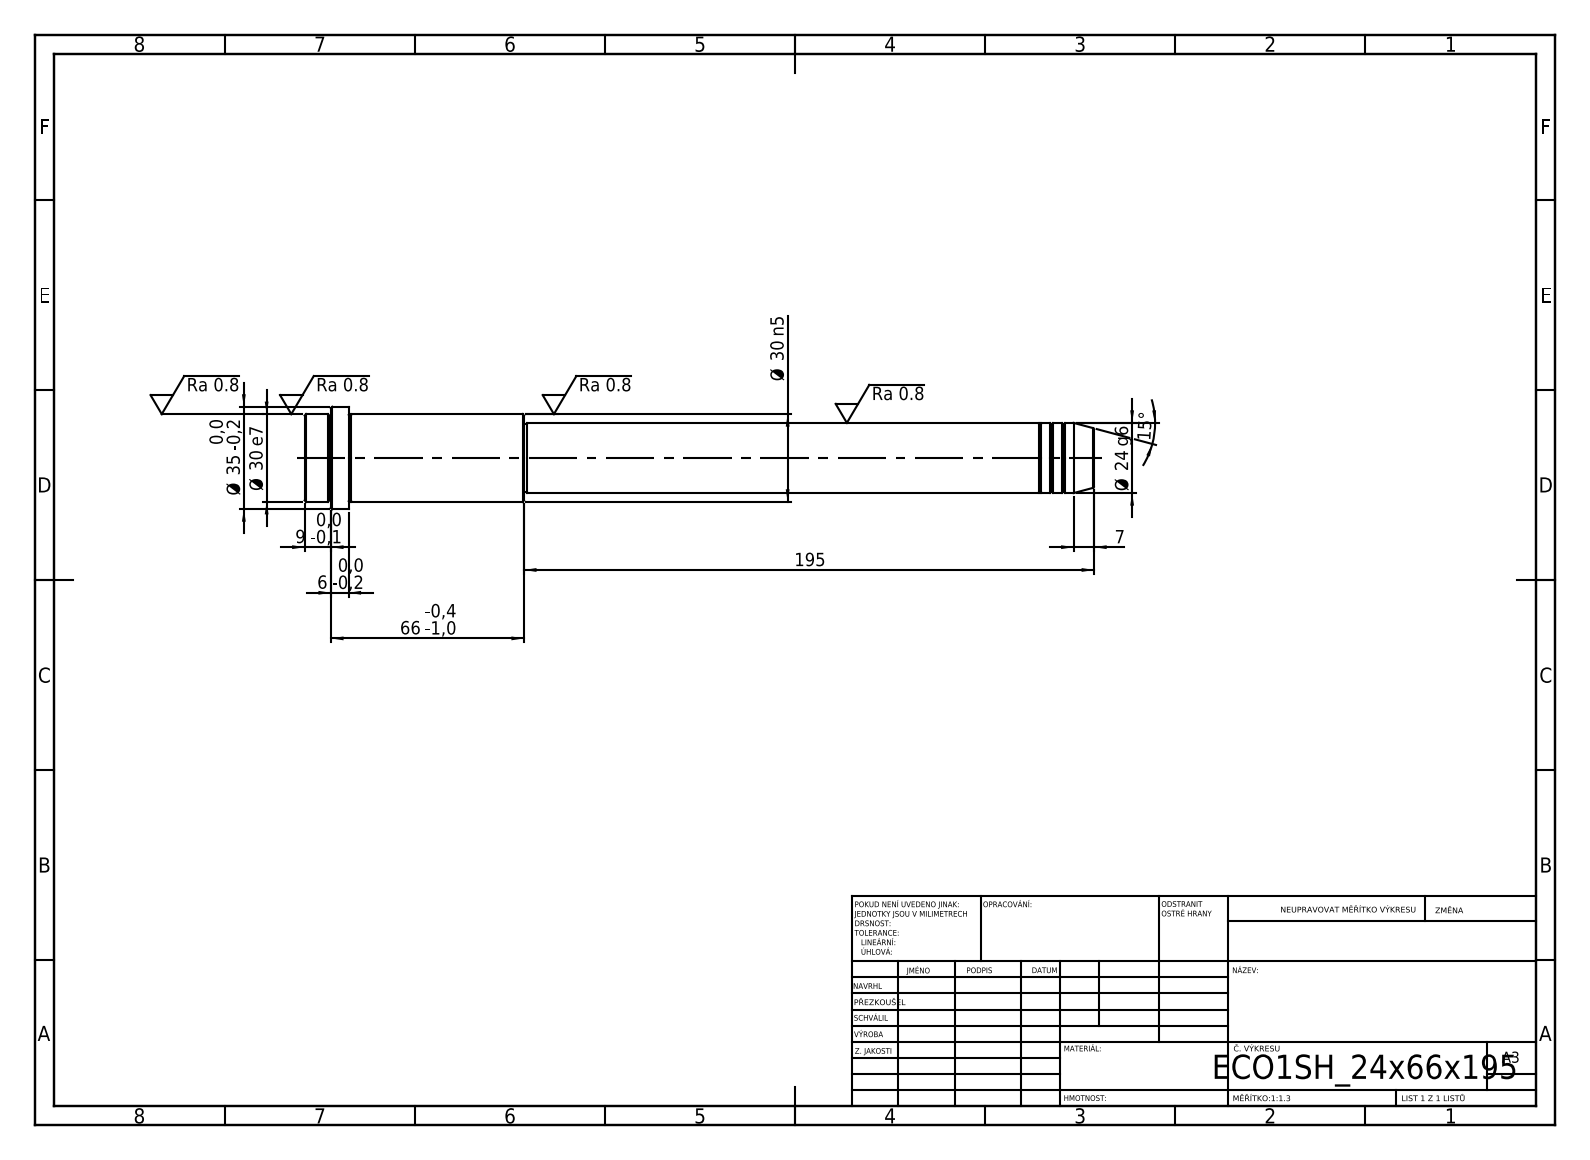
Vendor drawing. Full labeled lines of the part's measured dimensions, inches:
STEP written by: SolidWorks 2019 (CONFIG_CONTROL_DESIGN)
Units: inches
Bodies: 1 solid, 52 faces (6 planar, 16 cylindrical, 30 other)
Overall size (bounding box): 10.63 × 1.378 × 1.378
Volume: 8.669 in³ · Surface area: 36.94 in²
Round bosses / shafts (diameter × count): ⌀1.378 ×1, ⌀1.181 ×1, ⌀0.945 ×1, ⌀0.906 ×1
Main face-to-face distances: 10.63, 10.039, 0.591, 7.677, 2.362, 2.953, 10.276, 2.598, 0.236, 0.354
